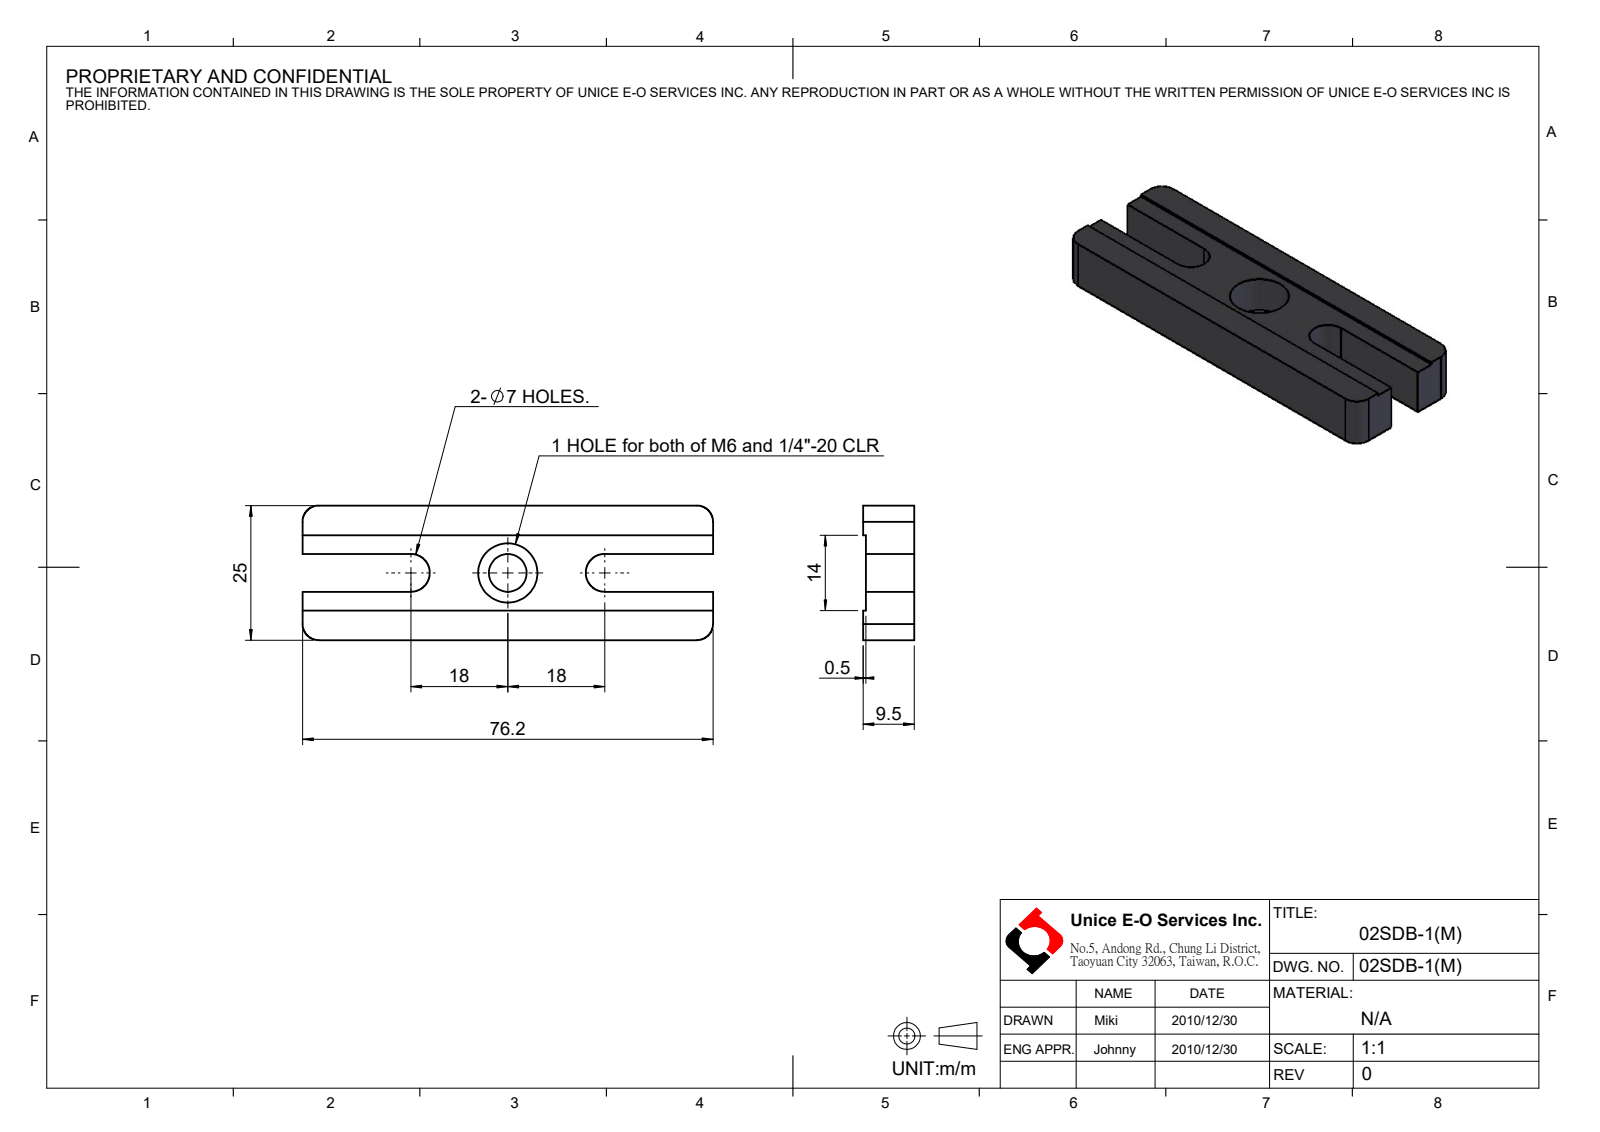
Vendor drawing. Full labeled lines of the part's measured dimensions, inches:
Part name (STEP PRODUCT): 02SDB-1(M)
STEP written by: SolidWorks 2016 (CONFIG_CONTROL_DESIGN)
Units: inches
Bodies: 1 solid, 27 faces (17 planar, 10 cylindrical, 0 other)
Overall size (bounding box): 3 × 0.984 × 0.374
Volume: 0.846 in³ · Surface area: 9.447 in²
Round holes (diameter × count): ⌀0.276 ×1, ⌀0.433 ×1
Partial cylindrical surfaces — rounded edges, fillets, slot ends (radius × count): R0.118 ×4, R0.138 ×2
Main face-to-face distances: 0.354, 0.374, 0.63, 0.984, 0.02, 0.276, 3, 0.217, 0.768, 0.138
